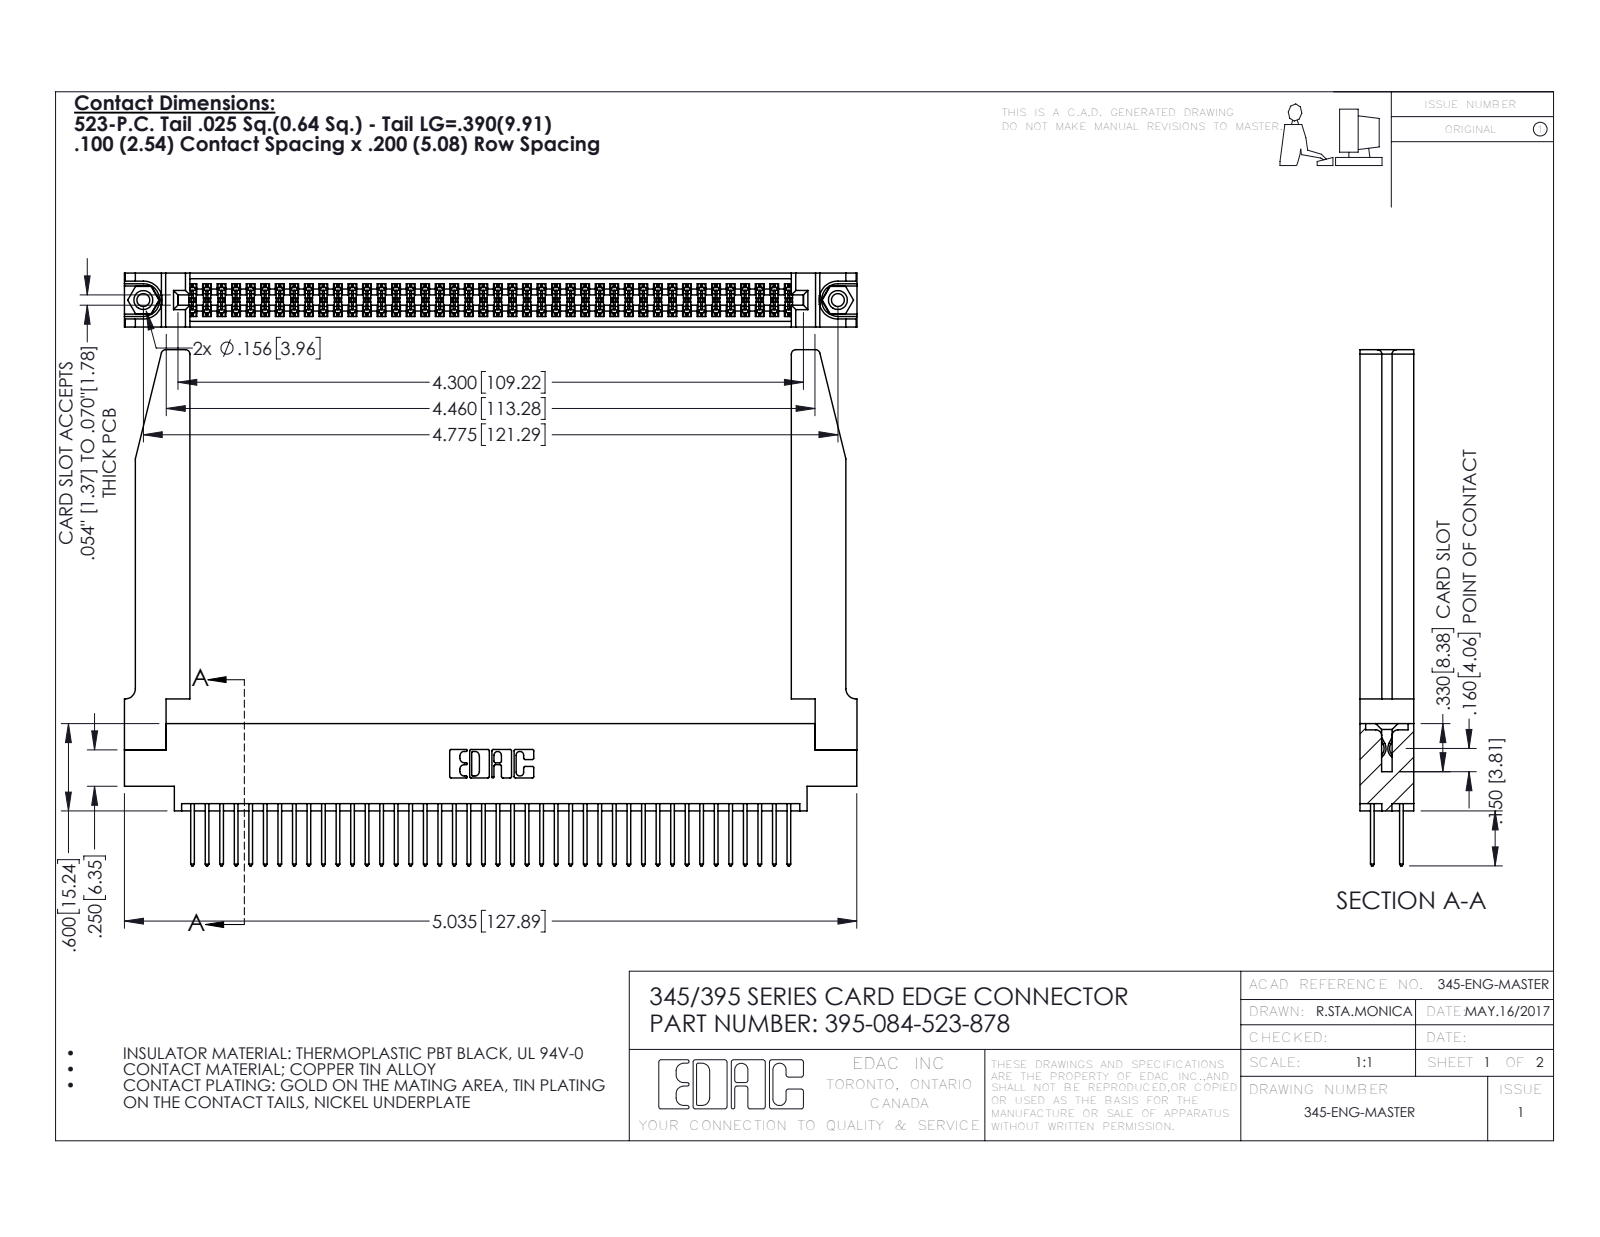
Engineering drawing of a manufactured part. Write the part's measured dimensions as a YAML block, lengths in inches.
part_name: "345 Part_0.170 Offset - 0.156 Dia-TH; 345-220-078_345-220-078; 345-292-001_345-293-123; 345-250-001_345-250-001-102 (+1 more)"
step_written_by: "SolidWorks 2016 (CONFIG_CONTROL_DESIGN)"
units: inches
bodies: {solids: 89, faces: 4564, planar: 2998, cylindrical: 1514, other: 52}
overall_size: [5.036, 3.547, 0.37]
volume: 1.236
surface_area: 40.62
round_holes:
  - {diameter: 0.089, count: 2}
  - {diameter: 0.125, count: 2}
  - {diameter: 0.156, count: 2}
  - {diameter: 0.064, count: 1}
round_bosses_or_shafts:
  - {diameter: 0.155, count: 2}
partial_cylinders:
  - {radius: 0.006, count: 126}
  - {radius: 0.01, count: 84}
  - {radius: 0.01, count: 22}
  - {radius: 0.03, count: 8}
  - {radius: 0.007, count: 6}
  - {radius: 0.031, count: 6}
  - {radius: 0.026, count: 3}
  - {radius: 0.014, count: 2}
face_to_face_distances: [0.072, 0.37, 0.298, 0.098, 0.272, 0.025, 0.2, 0.225, 0.175, 0.148]
hole_center_spacings: [0.27, 4.539, 4.775]
